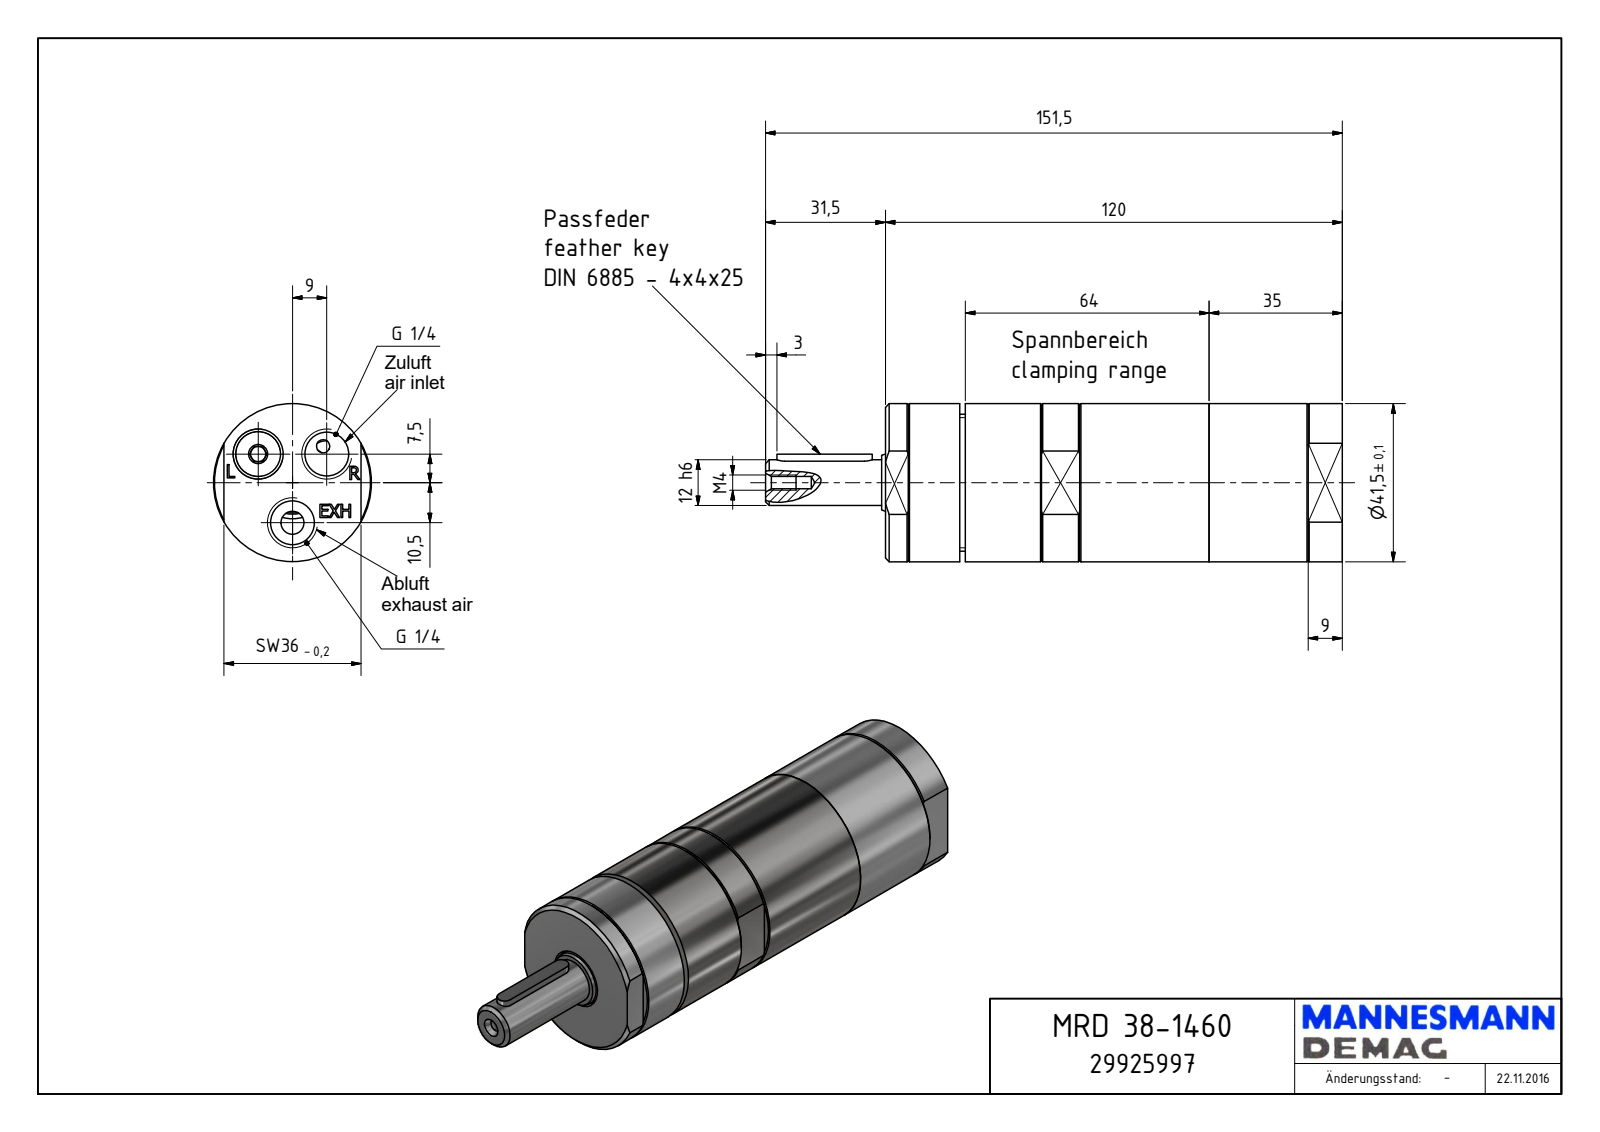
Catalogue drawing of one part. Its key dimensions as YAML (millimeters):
part_name: "MRD 38-1460_29925997"
step_written_by: "Autodesk Inventor 2018 (AUTOMOTIVE_DESIGN)"
units: millimeters
bodies: {solids: 1, faces: 152, planar: 100, cylindrical: 21, other: 31}
overall_size: [151.5, 41.5, 41.5]
volume: 161061
surface_area: 21830
round_holes:
  - {diameter: 11.45, count: 3}
  - {diameter: 3.24, count: 1}
  - {diameter: 4, count: 1}
  - {diameter: 16, count: 1}
round_bosses_or_shafts:
  - {diameter: 41.5, count: 1}
  - {diameter: 36, count: 1}
  - {diameter: 14.95, count: 1}
  - {diameter: 12, count: 1}
partial_cylinders:
  - {radius: 2, count: 2}
face_to_face_distances: [120, 1, 21, 37, 19.5, 1.5, 100.5, 99, 107.52, 88.02]
hole_center_spacings: [11.72, 20.12, 10.5, 18]
